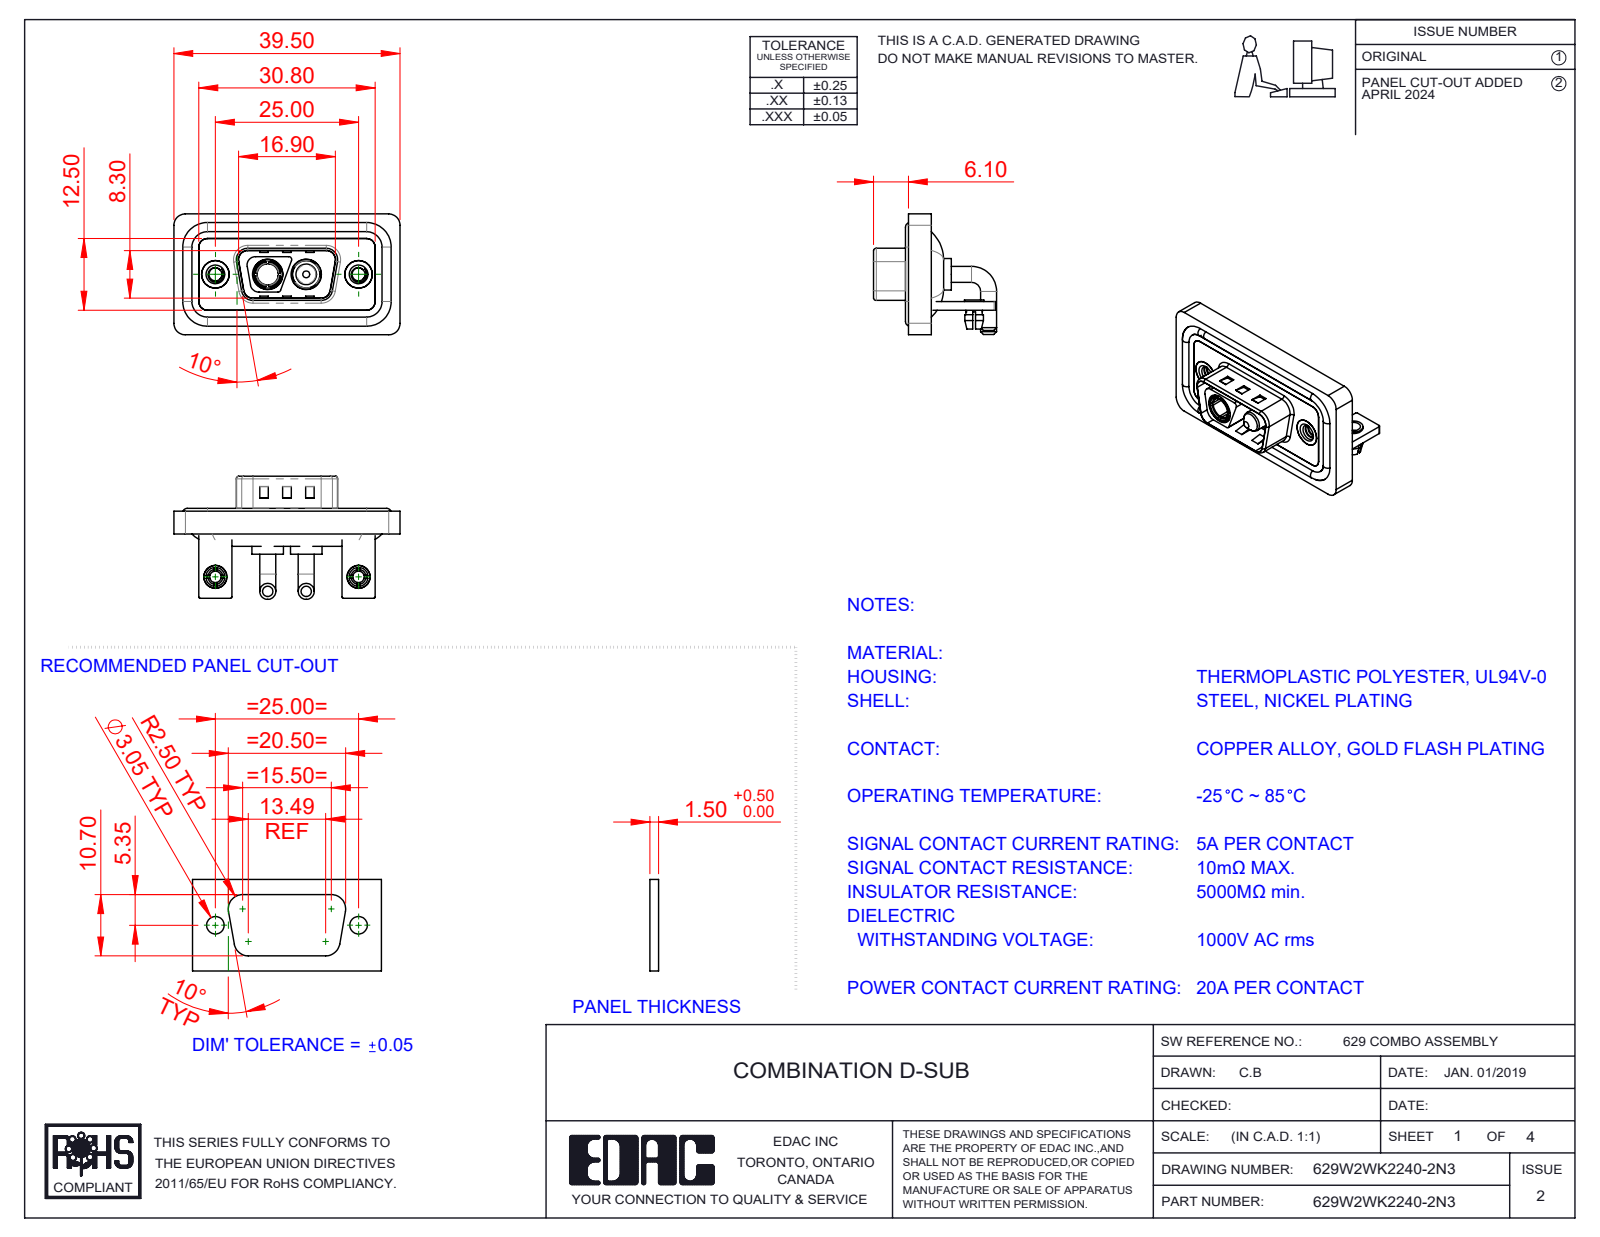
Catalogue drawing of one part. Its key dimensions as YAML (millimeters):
part_name: "629Combo Board Lock; 629Combo Shell Rear_09 Contacts; 629Combo Stabilizer Bracket; 629Combo Waterproof Housing_09 Contacts (+6 more)"
step_written_by: "SolidWorks 2023 (CONFIG_CONTROL_DESIGN)"
units: millimeters
bodies: {solids: 15, faces: 674, planar: 257, cylindrical: 281, other: 136}
overall_size: [39.5, 21.5, 21.1]
volume: 4996
surface_area: 8329
round_holes:
  - {diameter: 2, count: 2}
  - {diameter: 2.26, count: 2}
  - {diameter: 2.5, count: 2}
  - {diameter: 3.2, count: 2}
  - {diameter: 4, count: 2}
  - {diameter: 4.8, count: 2}
  - {diameter: 4.85, count: 2}
  - {diameter: 5, count: 2}
  - {diameter: 5.3, count: 2}
  - {diameter: 3.7, count: 1}
round_bosses_or_shafts:
  - {diameter: 2.8, count: 4}
  - {diameter: 1.6, count: 4}
  - {diameter: 5.5, count: 2}
  - {diameter: 5.2, count: 2}
  - {diameter: 4.9, count: 2}
  - {diameter: 4.75, count: 2}
  - {diameter: 4, count: 2}
  - {diameter: 3.75, count: 2}
partial_cylinders:
  - {radius: 1.5, count: 20}
  - {radius: 2, count: 19}
  - {radius: 0.25, count: 16}
  - {radius: 0.5, count: 11}
  - {radius: 1.6, count: 8}
  - {radius: 0.6, count: 4}
  - {radius: 0.65, count: 4}
  - {radius: 0.9, count: 4}
face_to_face_distances: [0.4, 1.5, 2.9, 0.8, 1.1, 1.2, 2.1, 1.6, 3.7, 2.5]
hole_center_spacings: [9.14, 15.86, 25, 6.72]
